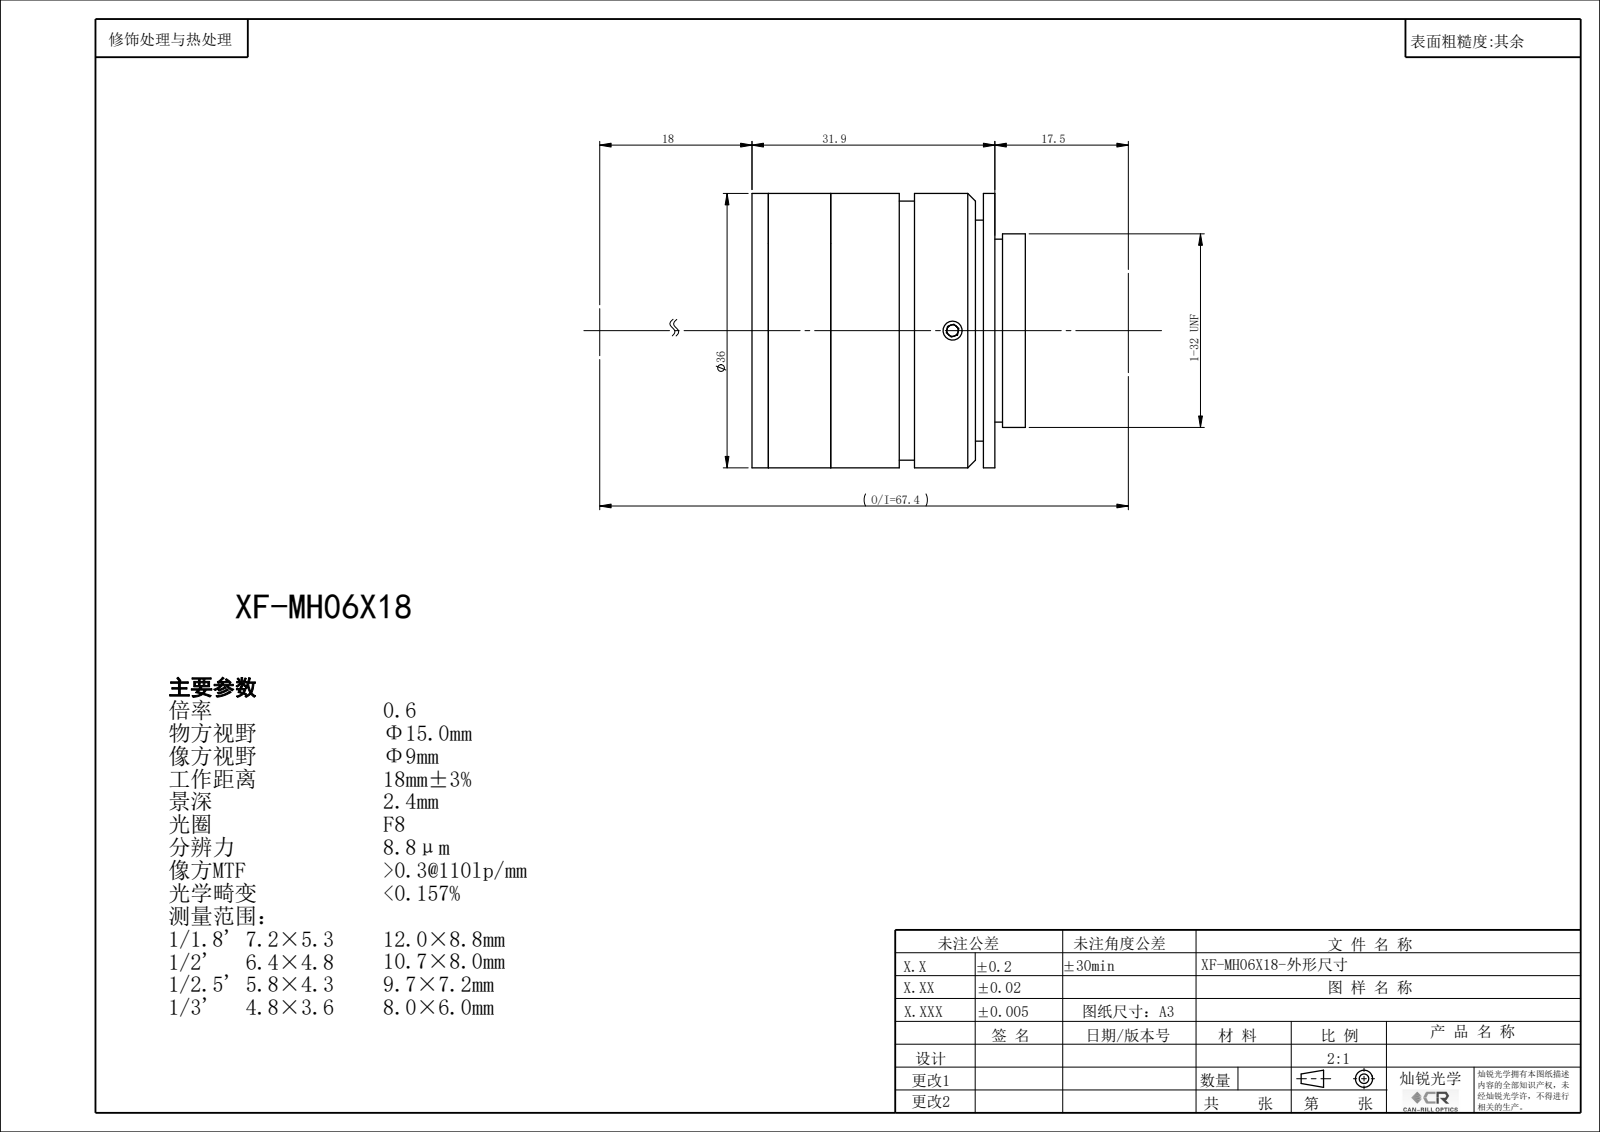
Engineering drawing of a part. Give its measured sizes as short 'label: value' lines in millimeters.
name: XF-MH06X18
written by: SolidWorks 2022 (CONFIG_CONTROL_DESIGN)
unit: mm
bodies: 0 solids, 111 faces (53 planar, 48 cylindrical, 10 other)
size: 36 × 36 × 35.88
holes: 3× ⌀2.5, 1× ⌀7, 1× ⌀8.4, 1× ⌀10, 1× ⌀12, 1× ⌀14, 1× ⌀16, 1× ⌀18, 1× ⌀20, 1× ⌀21.5, 1× ⌀22, 1× ⌀24
bosses: 1× ⌀36, 1× ⌀34, 1× ⌀25.4
face distances: 8.18, 10.33, 29.74, 21.56, 2.15, 31.89, 2, 1, 1.5, 30.39
